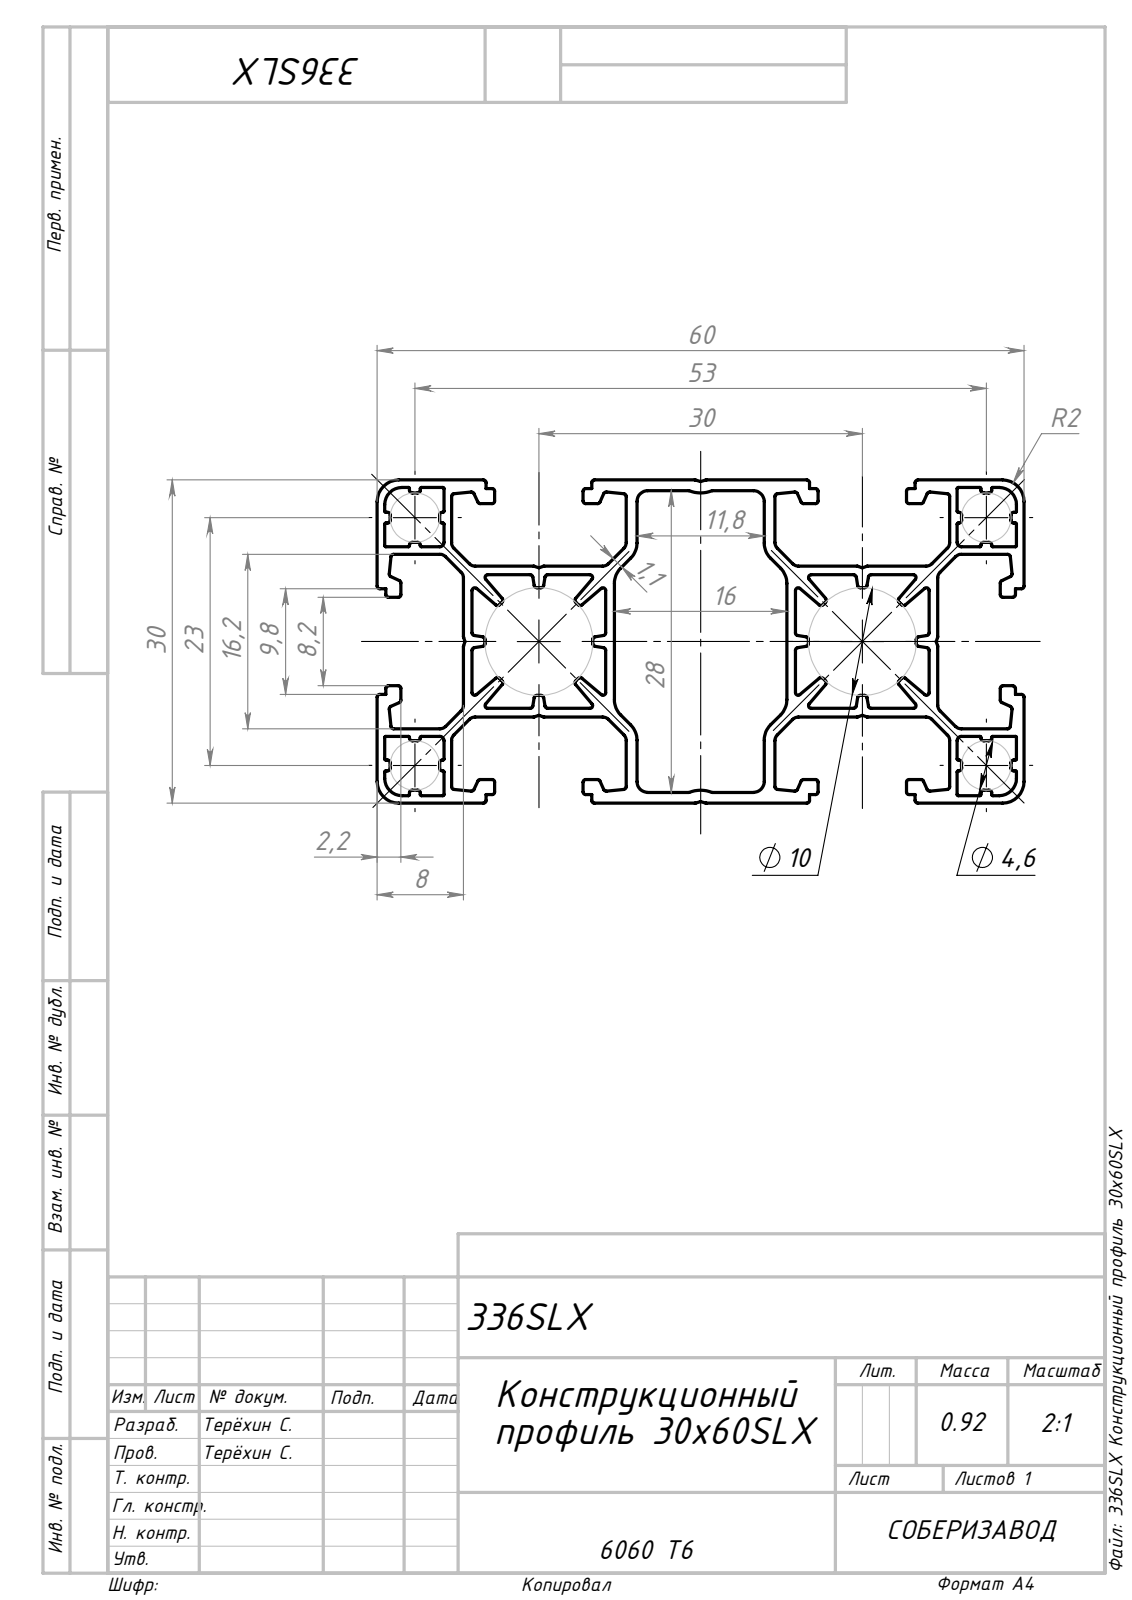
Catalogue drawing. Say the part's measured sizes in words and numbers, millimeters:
The part is named "336SL Конструкционный профиль 30х60SL_00; Сборка3". Its 3-D file was written by "SolidWorks 2022 (AUTOMOTIVE_DESIGN)". It is 1 solid with 610 faces: 264 planar, 346 cylindrical and 0 other. Overall it measures 1000 by 60 by 30 millimeters. Its volume is 341 003 cubic millimeters and its surface area 689 561 square millimeters. Partial cylindrical surfaces (rounded edges, fillets, slot ends): 184 of radius 0.25, 40 of radius 0.1, 24 of radius 0.75, 12 of radius 2, 4 of radius 0.4, 4 of radius 1, 4 of radius 1.6, 4 of radius 2.3. The main face-to-face distances are 30, 8, 0.8, 22, 1.1, 13.2, 21.2, 15.1, 0.7, 6.2.
